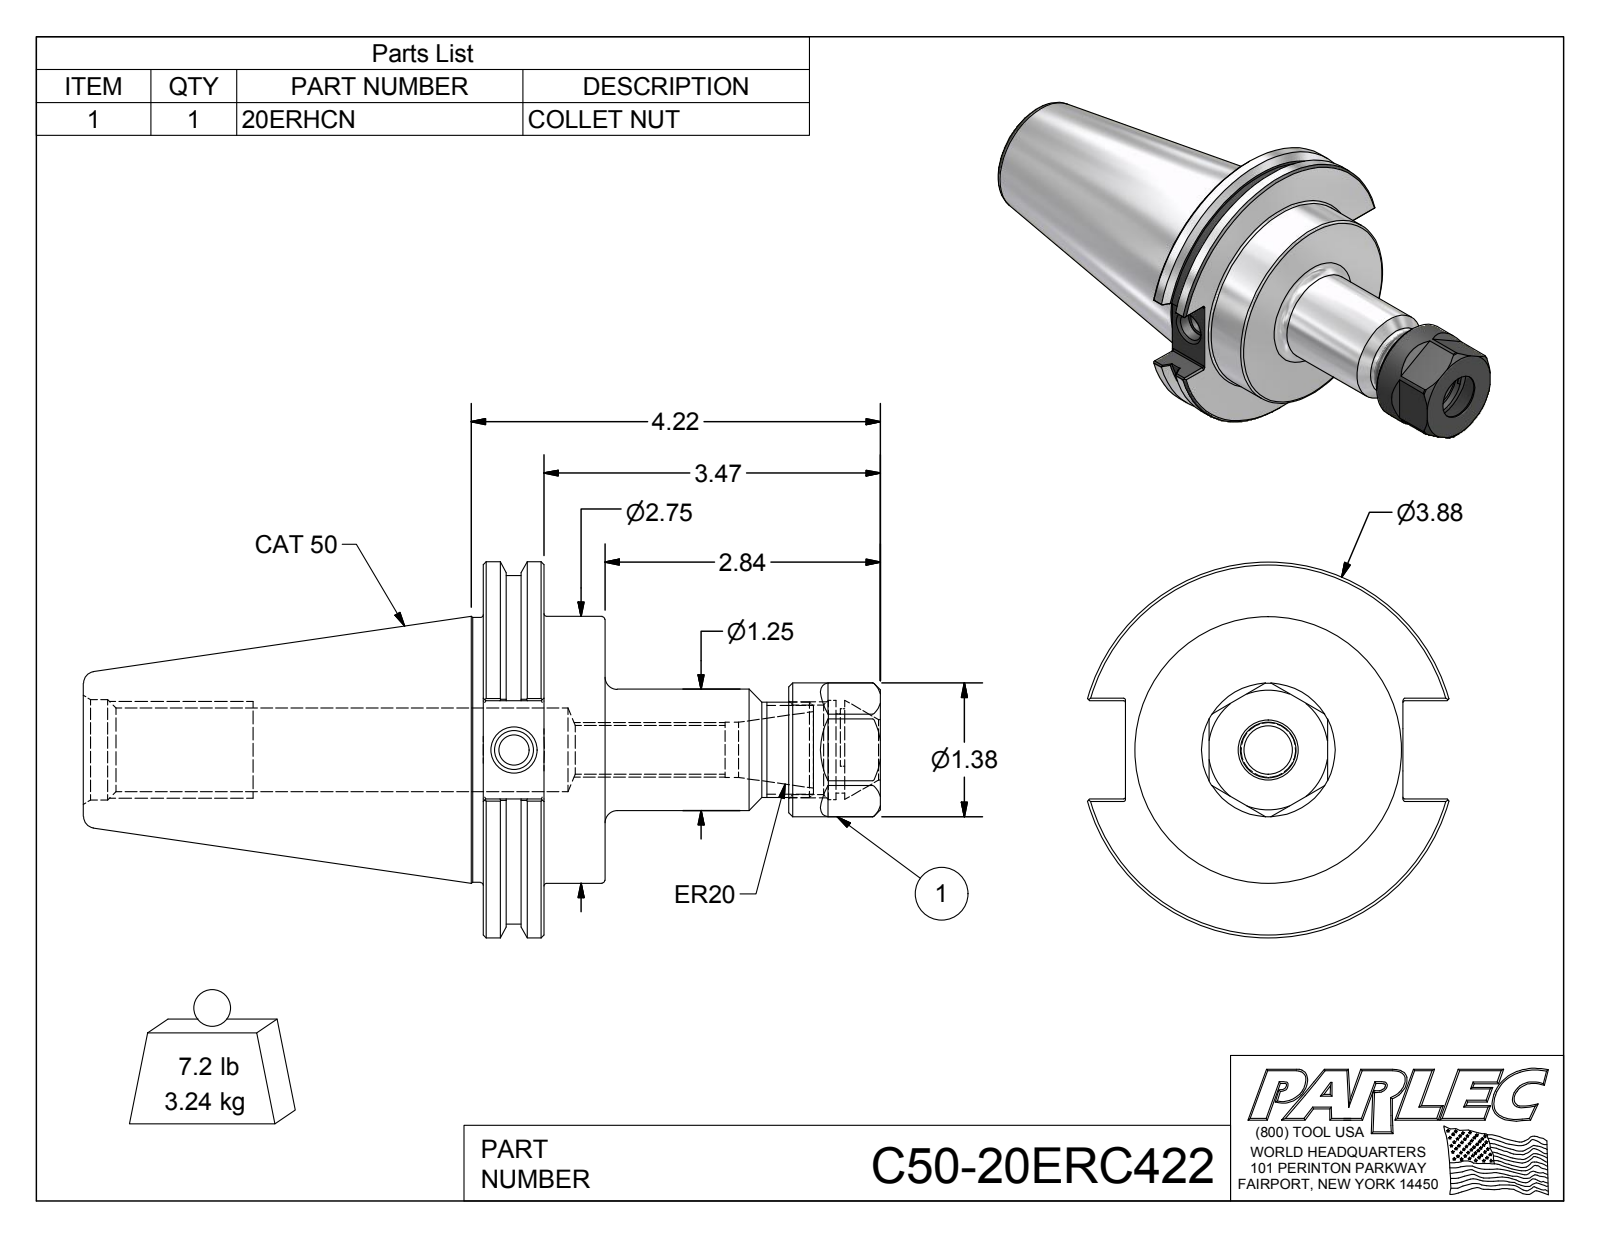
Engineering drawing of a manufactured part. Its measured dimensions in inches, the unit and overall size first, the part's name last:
Units: inches
Overall size (bounding box): 8.22 × 3.875 × 3.729
Round holes (diameter × count): ⌀0.315 ×1, ⌀0.399 ×1, ⌀0.502 ×1, ⌀0.57 ×1, ⌀0.62 ×1, ⌀0.82 ×1, ⌀0.865 ×1, ⌀0.925 ×1, ⌀1.024 ×1, ⌀1.038 ×1
Round bosses / shafts (diameter × count): ⌀3.875 ×1, ⌀3.594 ×1, ⌀2.75 ×1, ⌀2.73 ×1, ⌀1.378 ×1, ⌀1.25 ×1, ⌀0.984 ×1
Partial cylindrical surfaces — rounded edges, fillets, slot ends (radius × count): R0.02 ×12, R0.423 ×1
Main face-to-face distances: 0.625, 1.255, 0.63, 1.22, 4.095, 3.47, 2.84, 3.15, 2.525, 1.895
Hole centre spacings: 0.037
Volume: 25.38 in³ · Surface area: 95.33 in²
Bodies: 2 solids, 132 faces (50 planar, 34 cylindrical, 48 other)
Part name (STEP PRODUCT): C50-20ERC422; C50-20ER4-1; 20ERHCN
STEP written by: Autodesk Inventor 2012 (AUTOMOTIVE_DESIGN)
